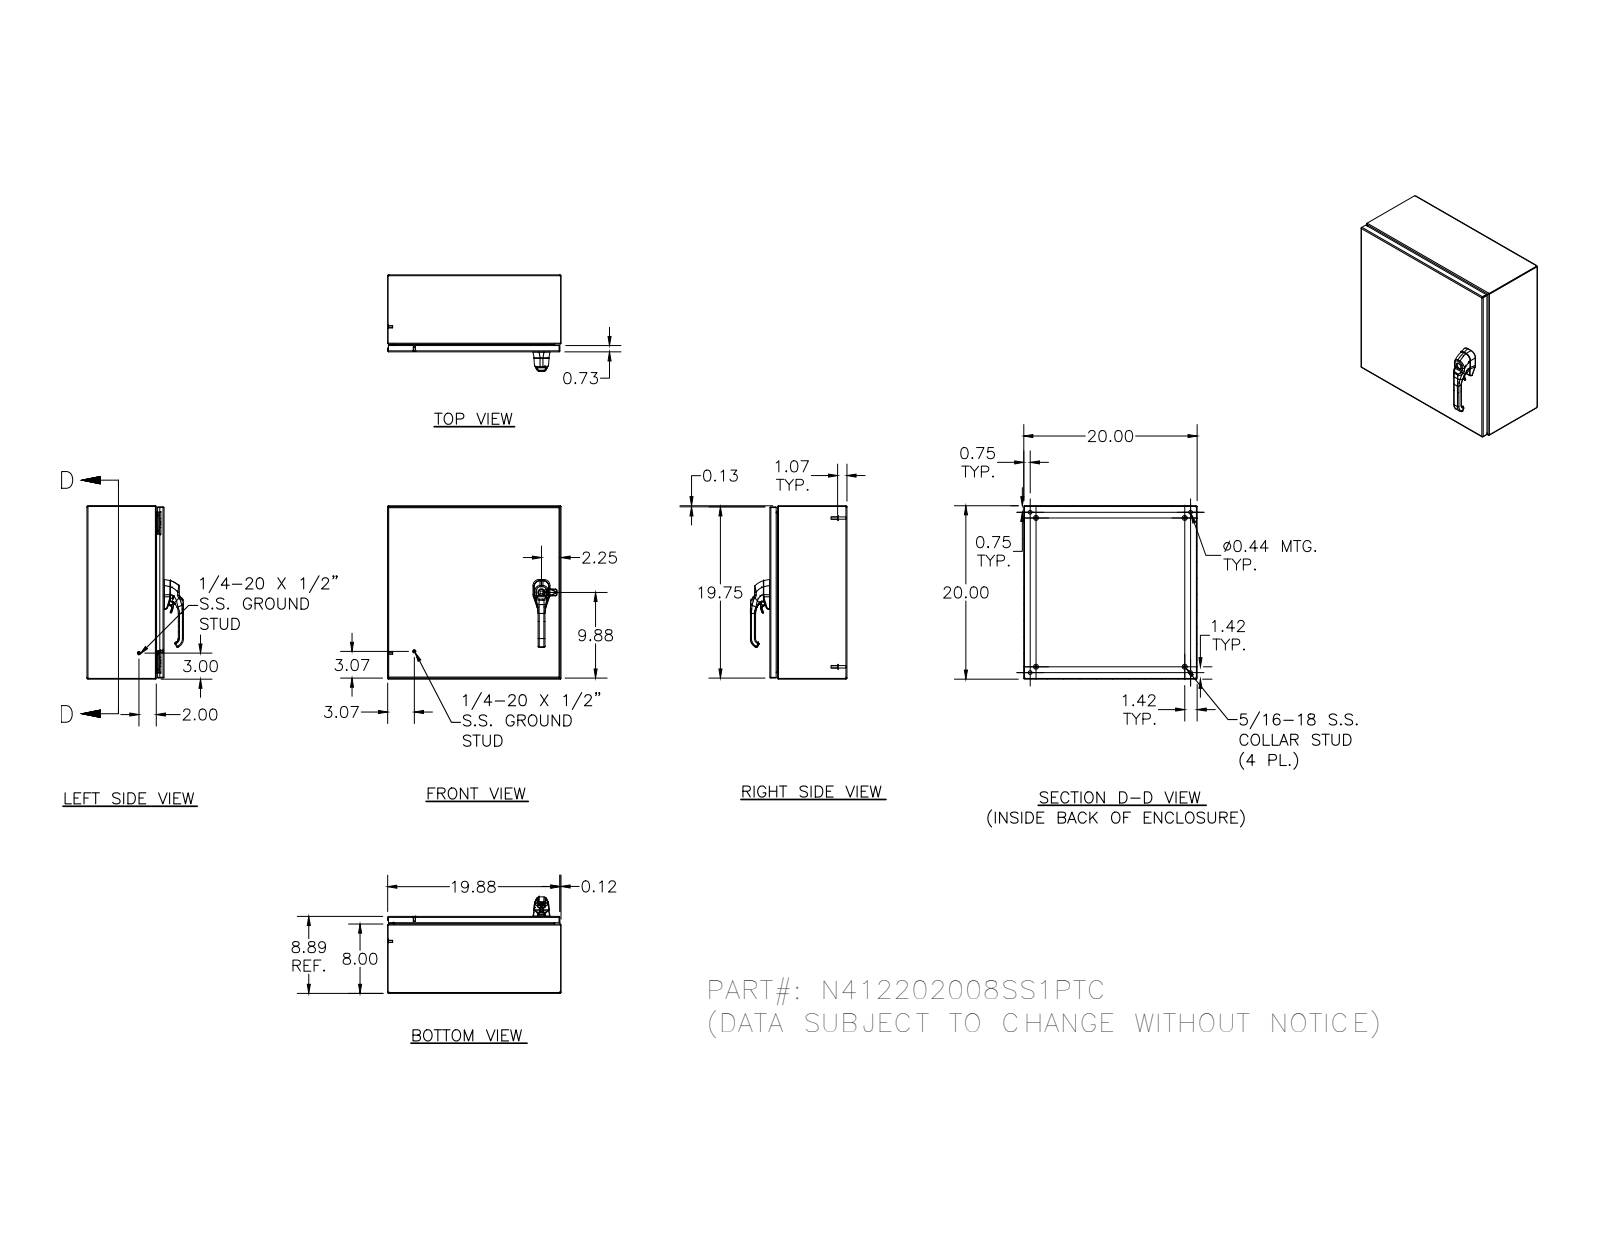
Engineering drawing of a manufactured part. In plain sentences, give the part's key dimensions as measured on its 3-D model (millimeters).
The part is named "N412202008SS1PTC; N412202008SS1PTCBKP; N4122020SS1PTCLID; HFW328176 (+8 more)". Its 3-D file was written by "Autodesk Inventor 2012 (AUTOMOTIVE_DESIGN)". It is 41 solids with 2782 faces: 882 planar, 1035 cylindrical and 865 other. Overall it measures 508 by 508 by 283.6 millimeters. Its volume is 2 058 000 cubic millimeters and its surface area 2 138 000 square millimeters. Round holes: 4 of diameter 2.4, 4 of diameter 3.9, 4 of diameter 4.2, 4 of diameter 4.4, 4 of diameter 4.8, 4 of diameter 11.1, 3 of diameter 5.4, 3 of diameter 7.1, 2 of diameter 4, 2 of diameter 8, 2 of diameter 10.2, 2 of diameter 10.5. Round bosses or shafts: 10 of diameter 6.4, 4 of diameter 14.3, 4 of diameter 9.1, 4 of diameter 8.1, 4 of diameter 7.6, 4 of diameter 7, 4 of diameter 6.5, 4 of diameter 4.2. Partial cylindrical surfaces (rounded edges, fillets, slot ends): 174 of radius 0.5, 101 of radius 0.3, 30 of radius 0.8, 26 of radius 1.3, 21 of radius 0.5, 20 of radius 2.7, 18 of radius 0.4, 14 of radius 2. The main face-to-face distances are 1.9, 224.6, 506.1, 226.5, 222.7, 504.2, 508, 201.3, 23.3, 18.8. The hole center spacings are 406.3, 469.9, 479.3, 0.4, 16.8, 406.5, 423.1, 0.5.
